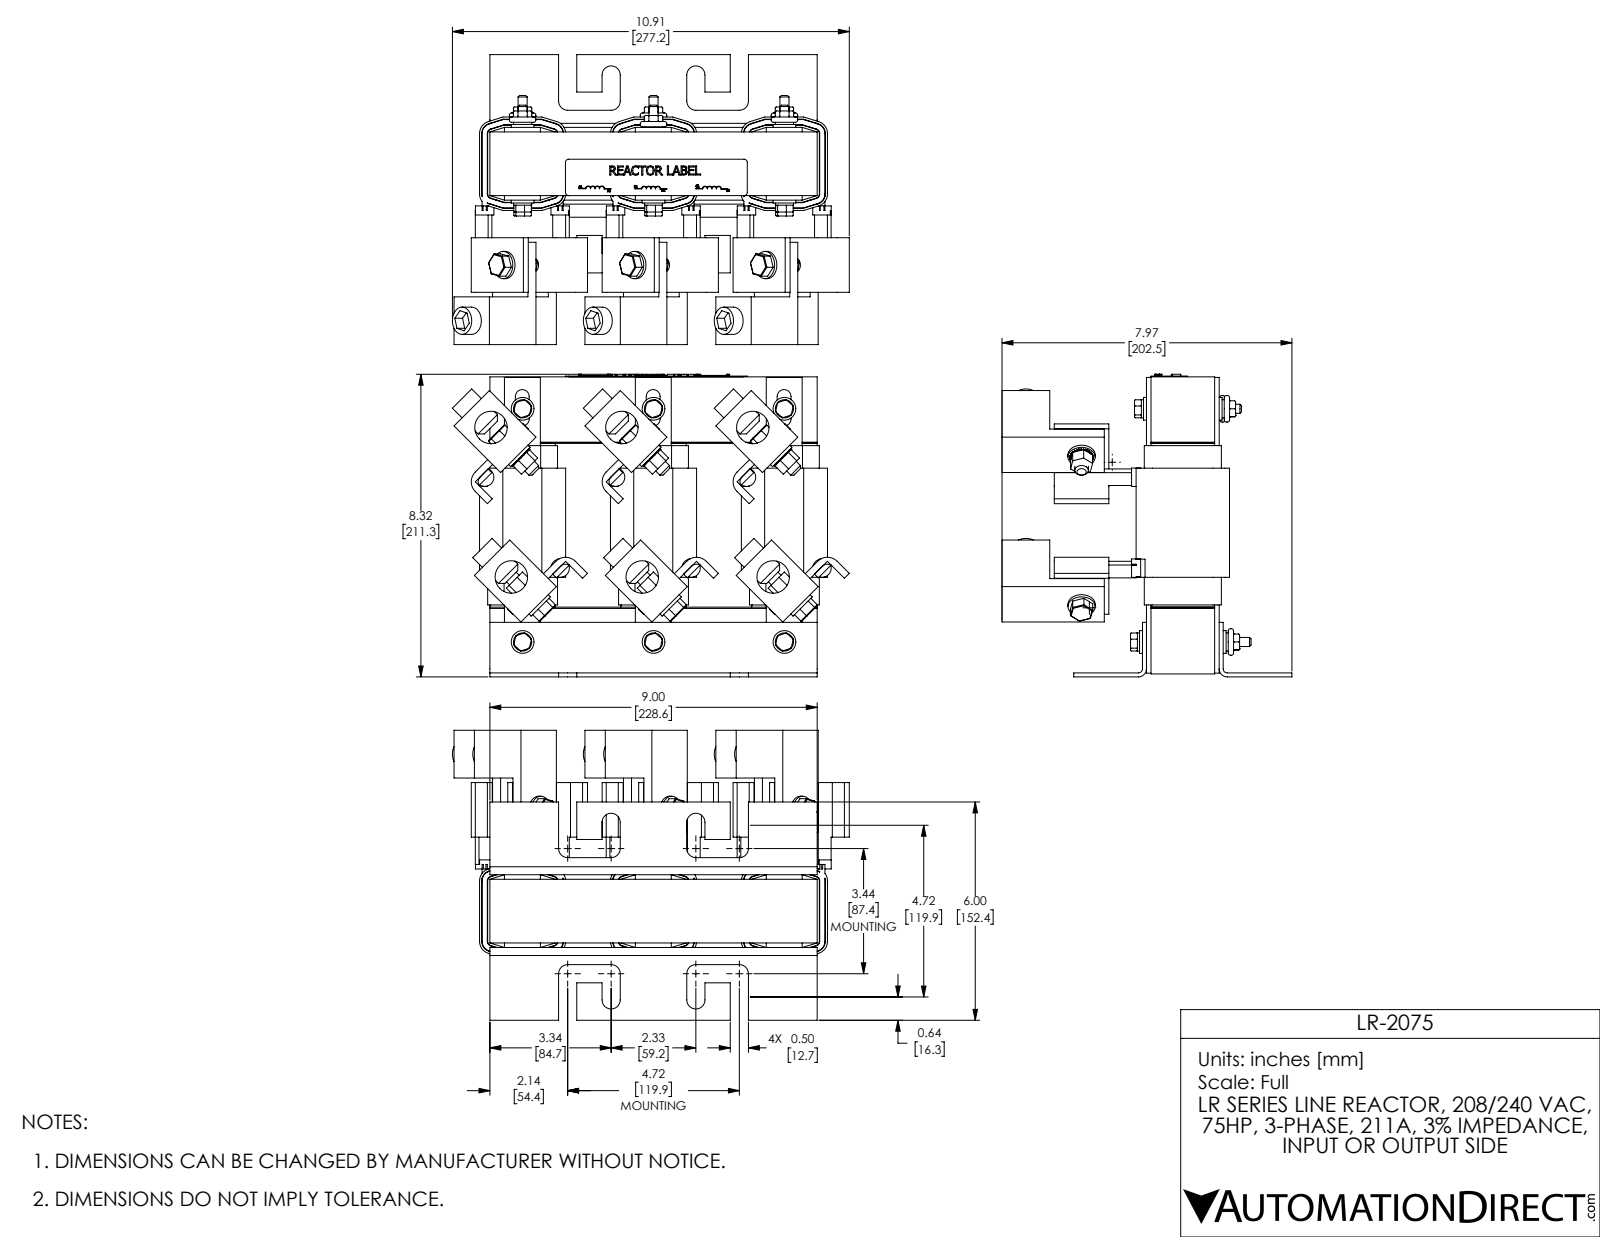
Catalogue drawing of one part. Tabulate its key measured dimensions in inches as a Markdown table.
| quantity | value |
| --- | --- |
| part name | LR-2075 LR-2100 |
| STEP written by | SolidWorks 2017 (AUTOMOTIVE_DESIGN) |
| units | inches |
| bodies | 85 solids, 2657 faces (1328 planar, 1103 cylindrical, 226 other) |
| overall size | 10.914 × 8.317 × 7.971 |
| volume | 161.1 in³ |
| surface area | 1 168 in² |
| round holes (diameter × count) | 0.242 × 6, 0.25 × 6, 0.281 × 6, 0.307 × 6, 0.344 × 6, 0.406 × 6, 0.44 × 6, 0.893 × 6, 0.375 × 5, 0.38 × 3, 0.375 × 2 |
| round bosses / shafts (diameter × count) | 0.75 × 13, 0.728 × 6, 0.625 × 6, 0.506 × 6, 0.5 × 6, 0.3 × 6, 0.375 × 1 |
| partial cylindrical surfaces (radius × count) | 0.03 × 192, 0.02 × 72, 0.03 × 72, 0.19 × 18, 0.077 × 12, 0.12 × 12, 0.13 × 12, 0.25 × 12 |
| main face-to-face distances | 0.06, 3.6, 0.154, 2.545, 0.224, 0.07, 0.144, 1.875, 0.125, 0.214 |
| hole center spacings | 3.6, 2.546, 7.2, 7.351, 0.037, 1.011, 1.813, 2.509 |
